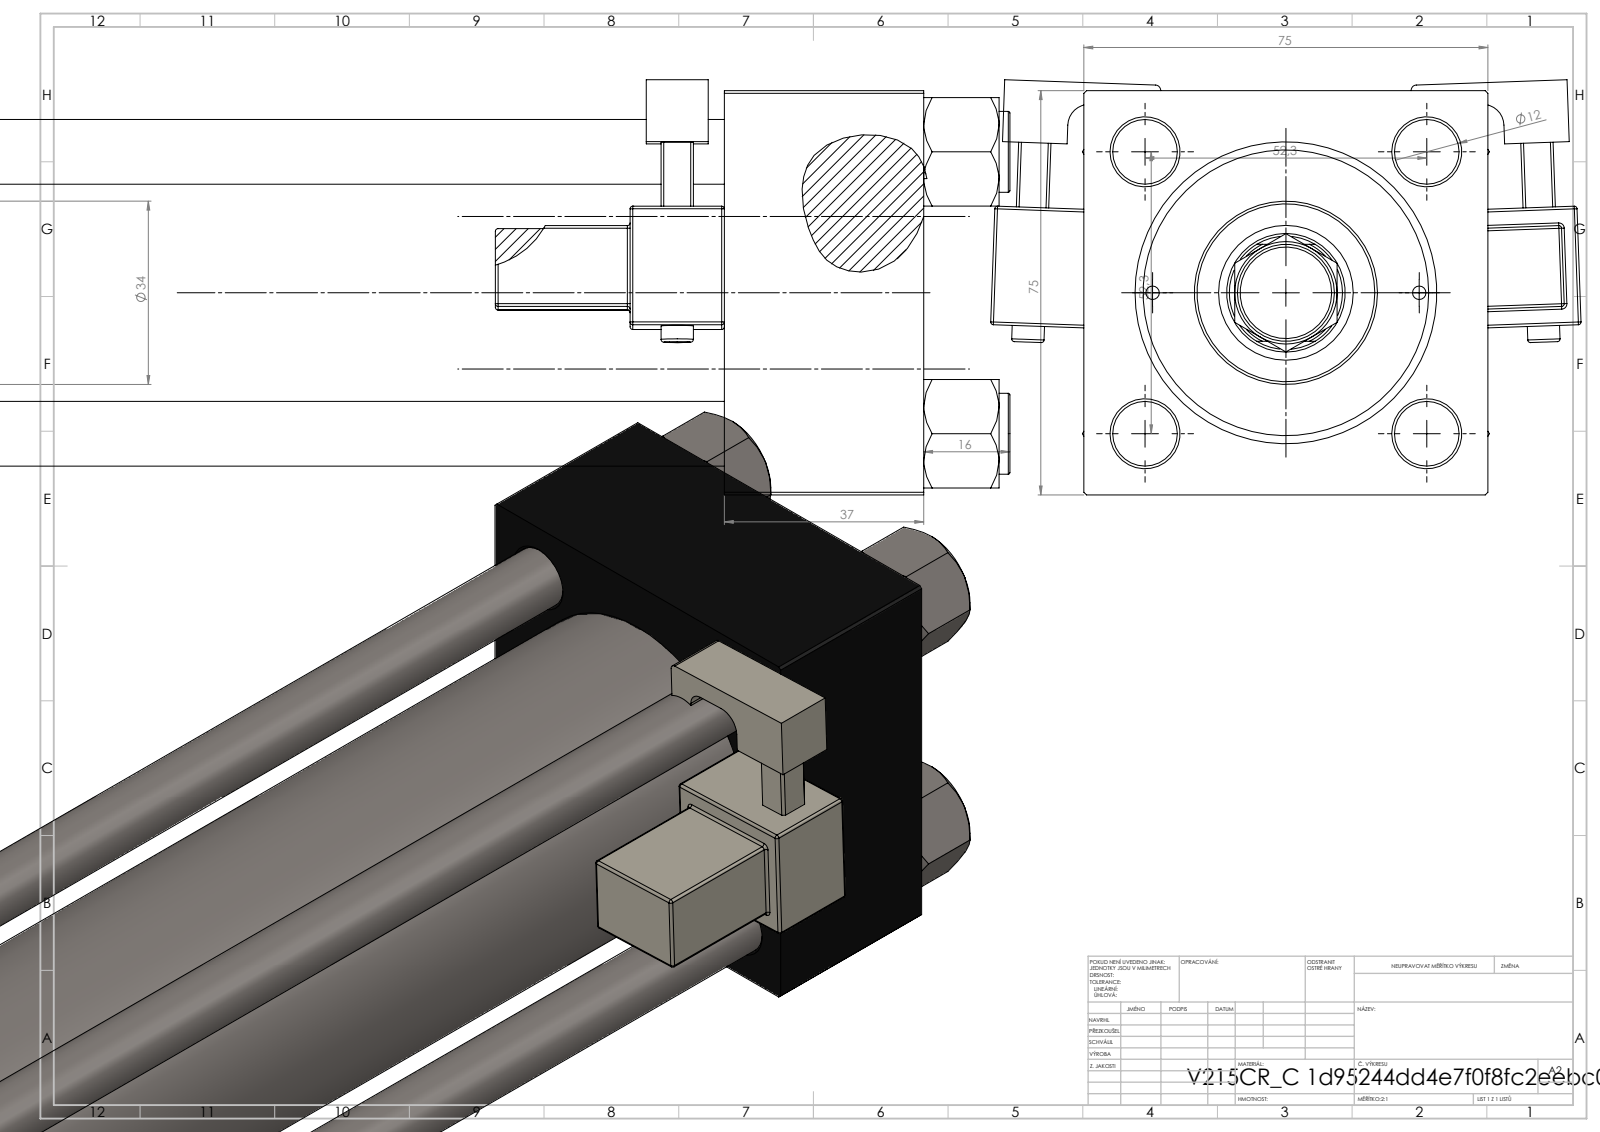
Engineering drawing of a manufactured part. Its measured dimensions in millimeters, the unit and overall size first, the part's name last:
Units: millimetres
Overall size (bounding box): 408 × 109.57 × 77.03
Round holes (diameter × count): ⌀12 ×4, ⌀2.5 ×2, ⌀7 ×2, ⌀20.96 ×2, ⌀30 ×2, ⌀10.5 ×1, ⌀22 ×1, ⌀25 ×1, ⌀41 ×1, ⌀50 ×1, ⌀53 ×1
Round bosses / shafts (diameter × count): ⌀15 ×4, ⌀6 ×2, ⌀56 ×1, ⌀34 ×1, ⌀18 ×1, ⌀11 ×1
Partial cylindrical surfaces — rounded edges, fillets, slot ends (radius × count): R0.5 ×48, R1 ×2, R2.5 ×2, R4 ×2, R10.5 ×1
Main face-to-face distances: 75, 37, 334, 297, 275, 238, 59, 305.3, 268.3, 30.3
Hole centre spacings: 26.19, 36.98, 52.3, 57.22, 24.75, 73.96, 49.5, 273.5
Volume: 945 896 mm³ · Surface area: 261 856 mm²
Bodies: 14 solids, 1360 faces (602 planar, 154 cylindrical, 604 other)
Part name (STEP PRODUCT): V215CR_C_TYCINKA; V215_VC_A; V215CR_VCP_C; V215CR_MSU (+3 more)
STEP written by: SolidWorks 2019 (CONFIG_CONTROL_DESIGN)
